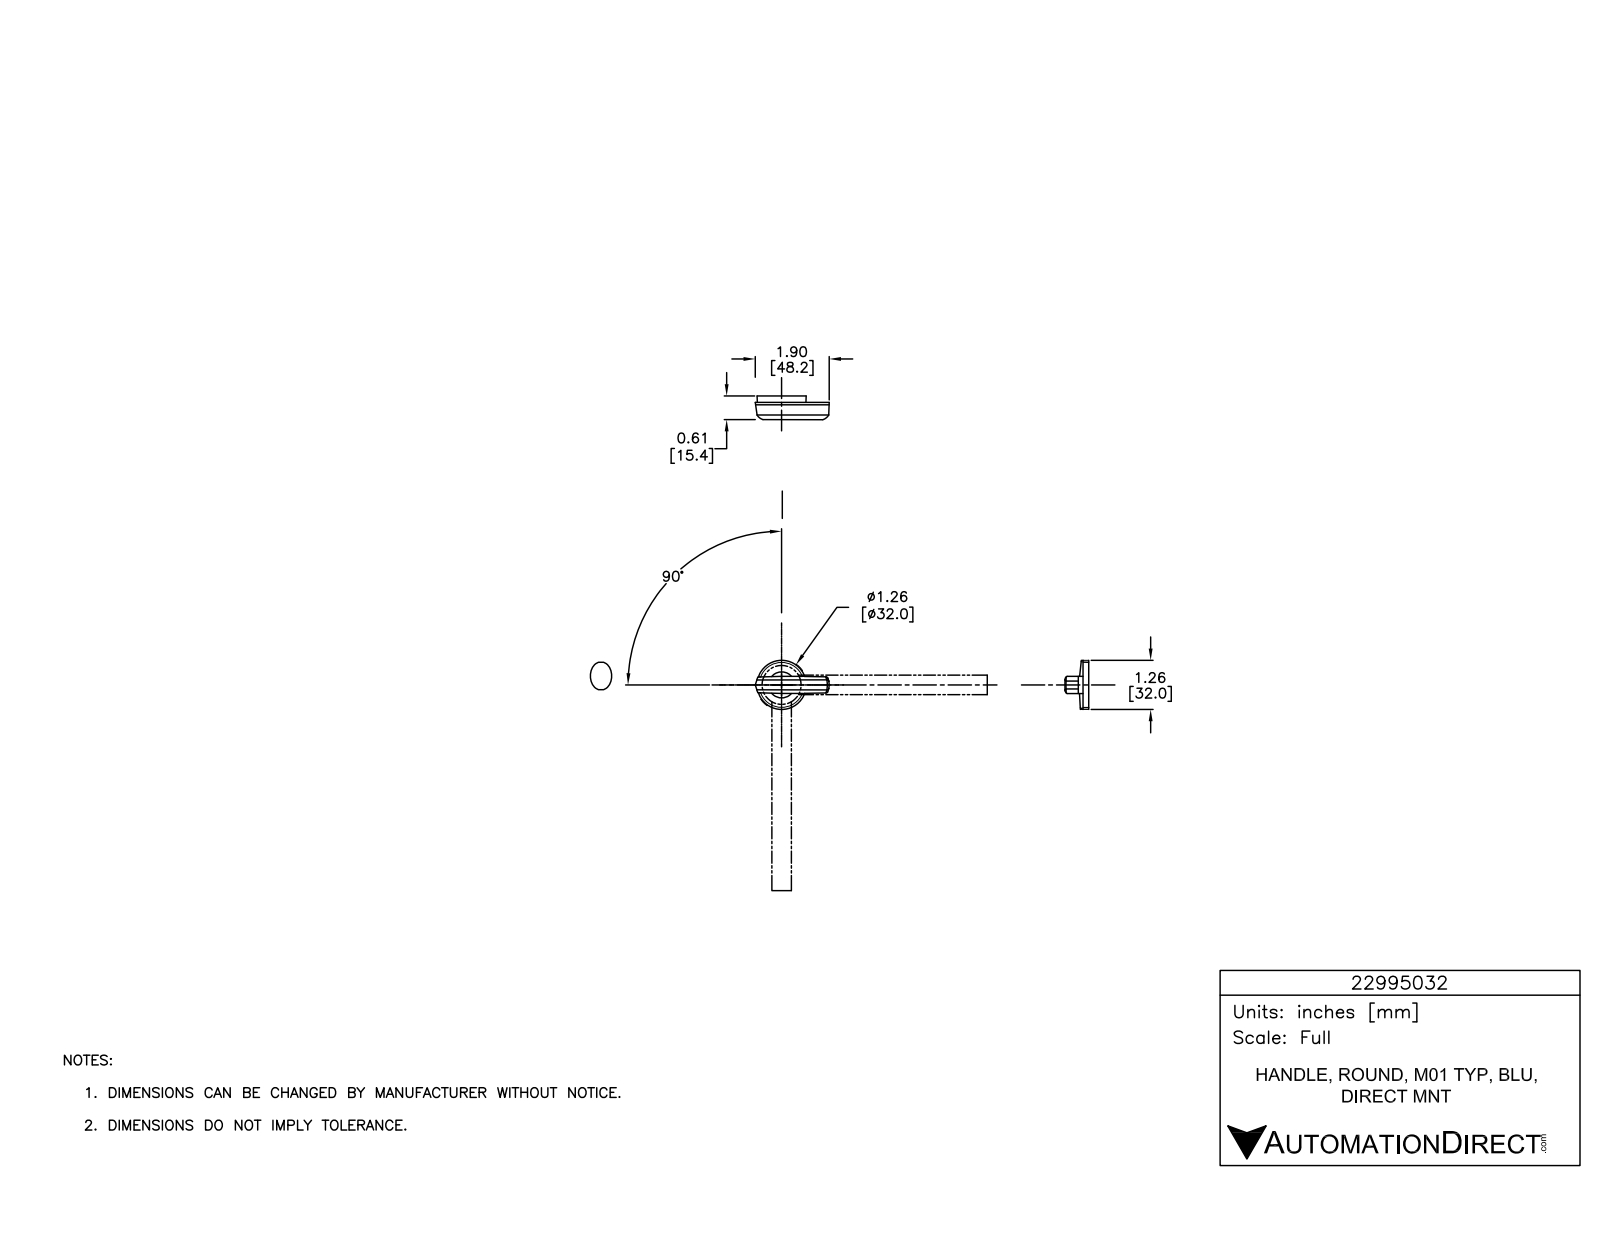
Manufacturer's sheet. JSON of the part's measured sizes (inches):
{"part_name": "22995032", "step_written_by": "SolidWorks 2015 (AUTOMOTIVE_DESIGN)", "units": "inches", "bodies": {"solids": 1, "faces": 20, "planar": 3, "cylindrical": 3, "other": 14}, "overall_size": [1.921, 1.244, 0.61], "volume_in3": 0.469, "surface_area_in2": 5.014, "round_bosses_or_shafts": [[1.244, 1]], "partial_cylinders_radius": [[0.433, 1]], "face_to_face_distances": [0.177]}
